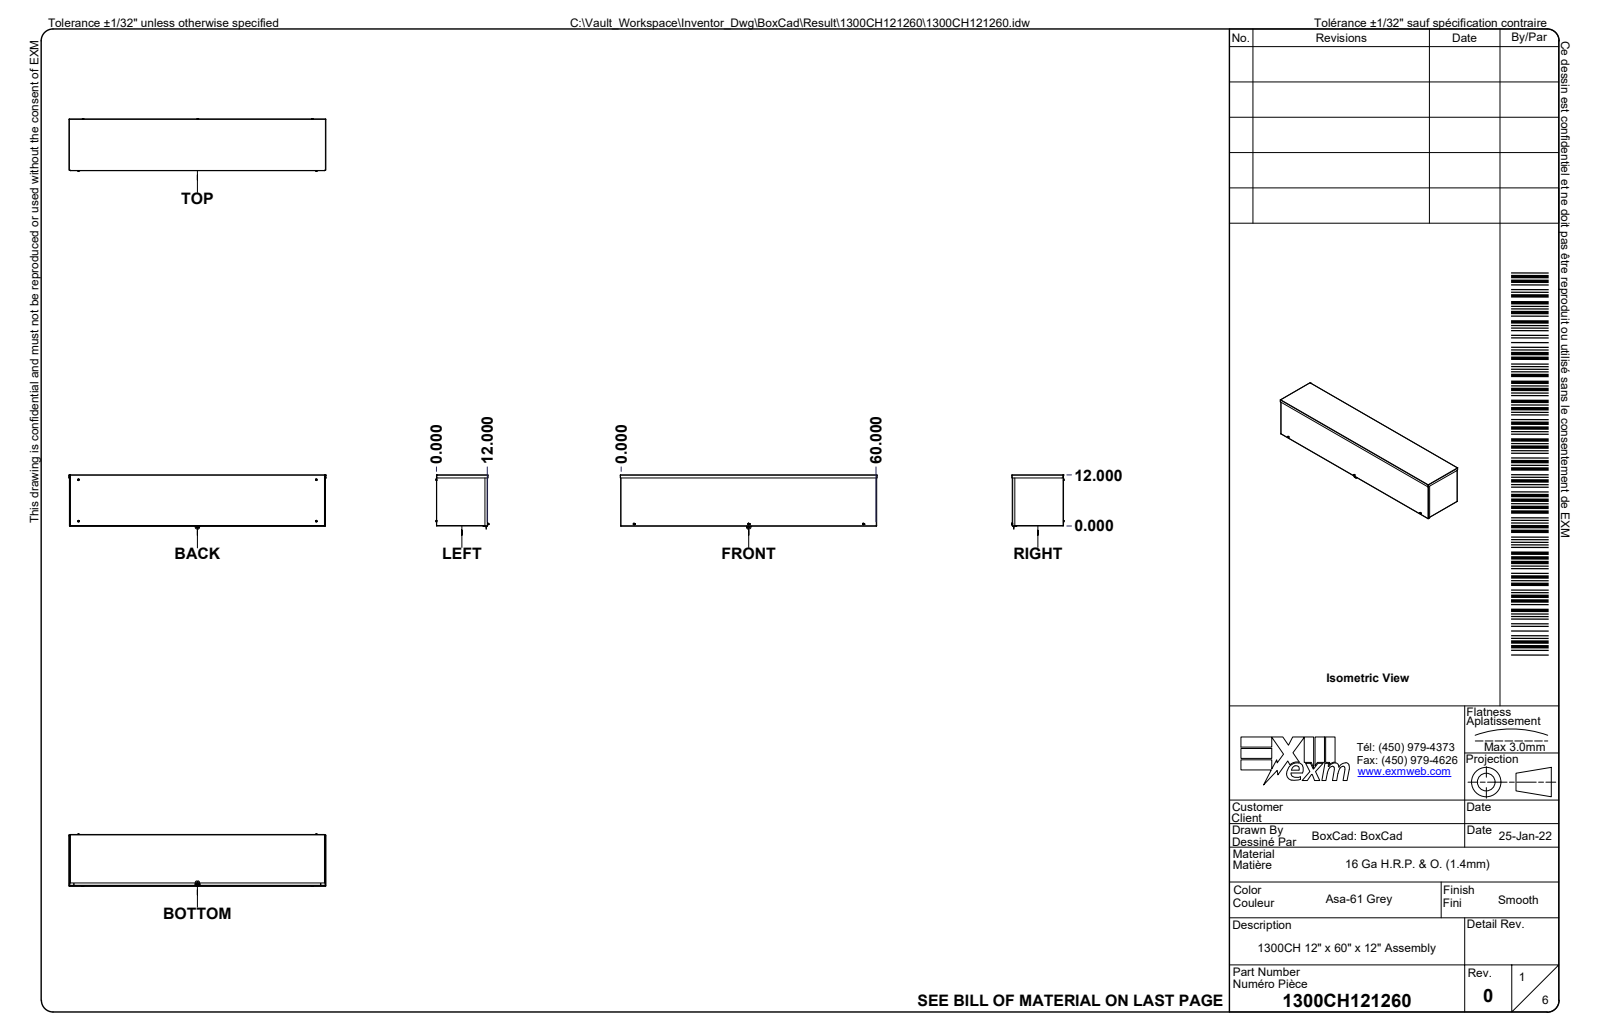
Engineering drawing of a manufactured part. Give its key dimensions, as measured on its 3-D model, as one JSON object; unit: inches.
{"part_name": "1300CH121260; 1300CH121260B; 1300CH121260B-P; 1300CH121260BR-P (+8 more)", "step_written_by": "Autodesk Inventor 2024 (AUTOMOTIVE_DESIGN)", "units": "inches", "bodies": {"solids": 21, "faces": 2815, "planar": 1585, "cylindrical": 288, "other": 942}, "overall_size": [60.46, 12.717, 12.28], "volume_in3": 179.3, "surface_area_in2": 6788, "round_holes": [[0.29, 7], [0.03, 4], [0.165, 4], [0.177, 4], [0.187, 4], [0.033, 2], [0.043, 1], [0.118, 1], [0.138, 1], [0.173, 1], [0.236, 1], [0.312, 1]], "round_bosses_or_shafts": [[0.374, 3], [0.189, 3], [0.126, 3], [0.03, 2], [1.25, 1], [1.142, 1], [0.3, 1], [0.25, 1]], "partial_cylinders_radius": [[0.02, 42], [0.031, 25], [0.004, 24], [0.084, 24], [0.012, 12], [0.25, 9], [0.145, 8], [0.094, 4]], "face_to_face_distances": [0.053, 11.947, 12, 11.894, 12.053, 59.947, 60, 59.894, 0.074, 12.117], "hole_center_spacings": [56, 56.843, 27, 29.882, 30.187, 1.214, 9.75, 28.008]}
